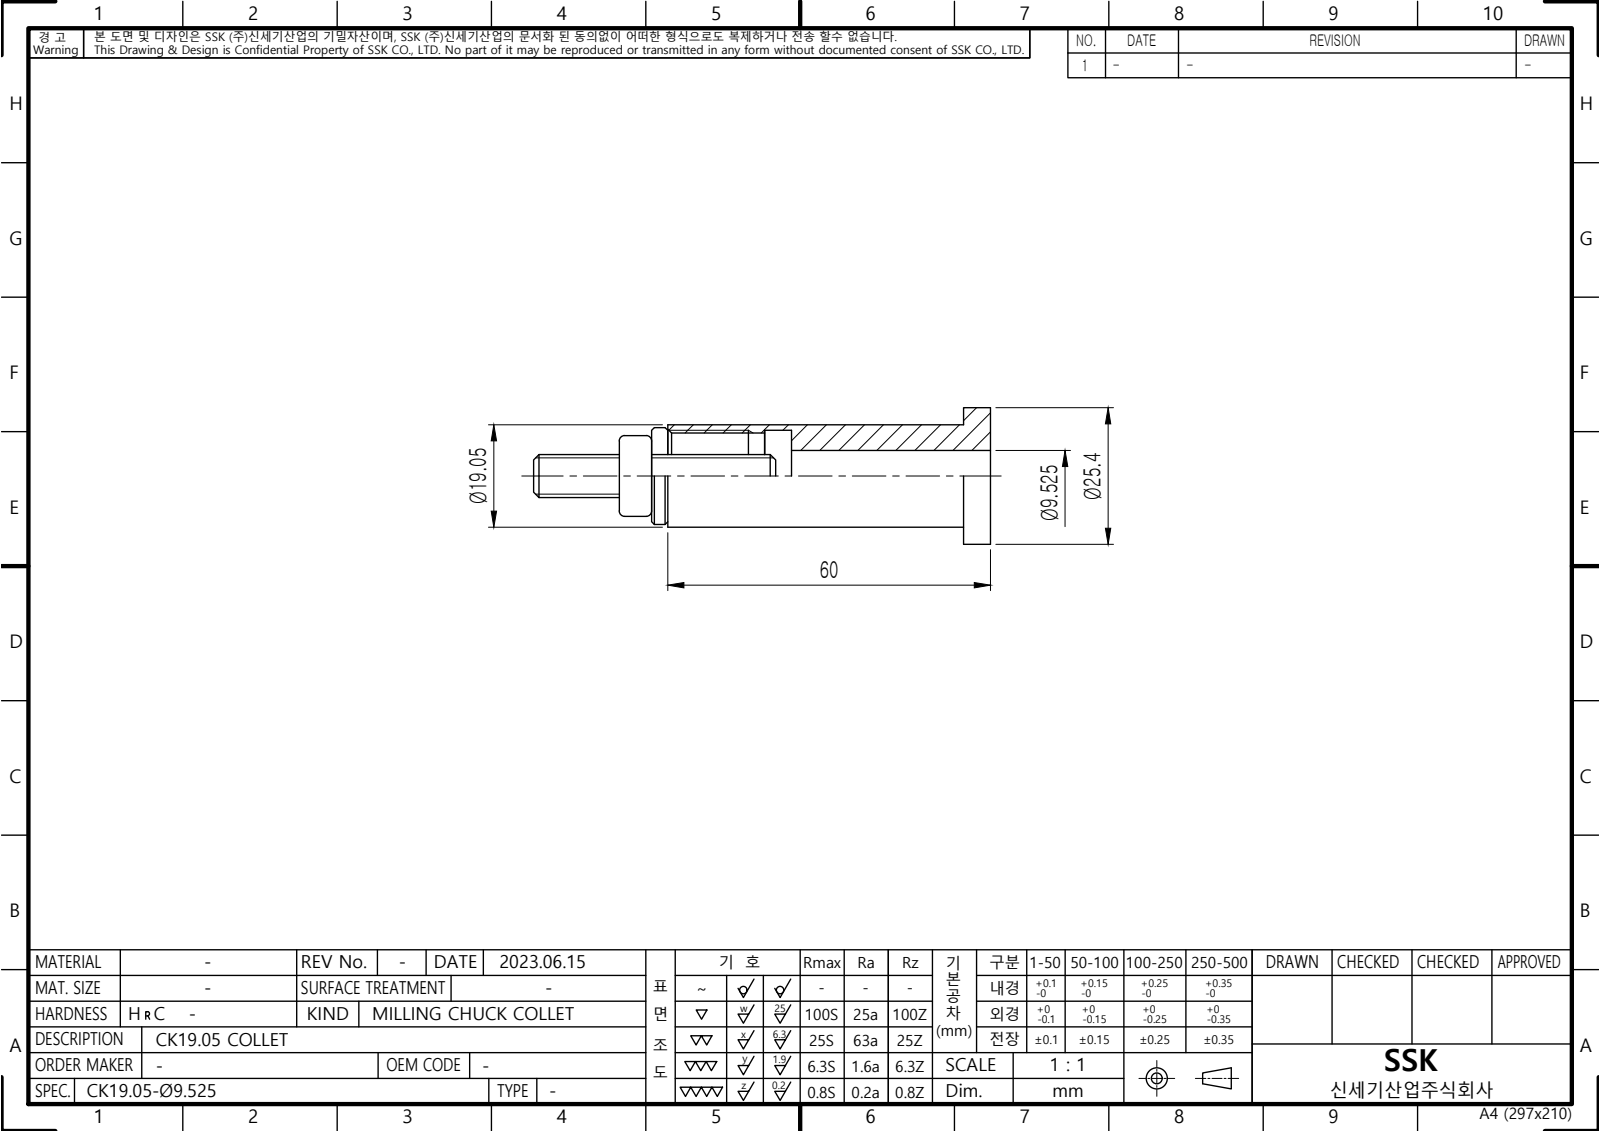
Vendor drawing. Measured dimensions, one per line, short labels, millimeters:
name: LO-CK19.05-9.525
written by: Autodesk Inventor 2022 (AUTOMOTIVE_DESIGN)
unit: mm
bodies: 1 solid, 10 faces (5 planar, 5 cylindrical, 0 other)
size: 60 × 25.4 × 25.4
volume: 10 857 mm³; area: 6 892 mm²
holes: 1× ⌀9.53, 1× ⌀15.92, 1× ⌀17
bosses: 1× ⌀25.4, 1× ⌀19.05
face distances: 5, 37, 32, 23, 55, 60, 18, 42
